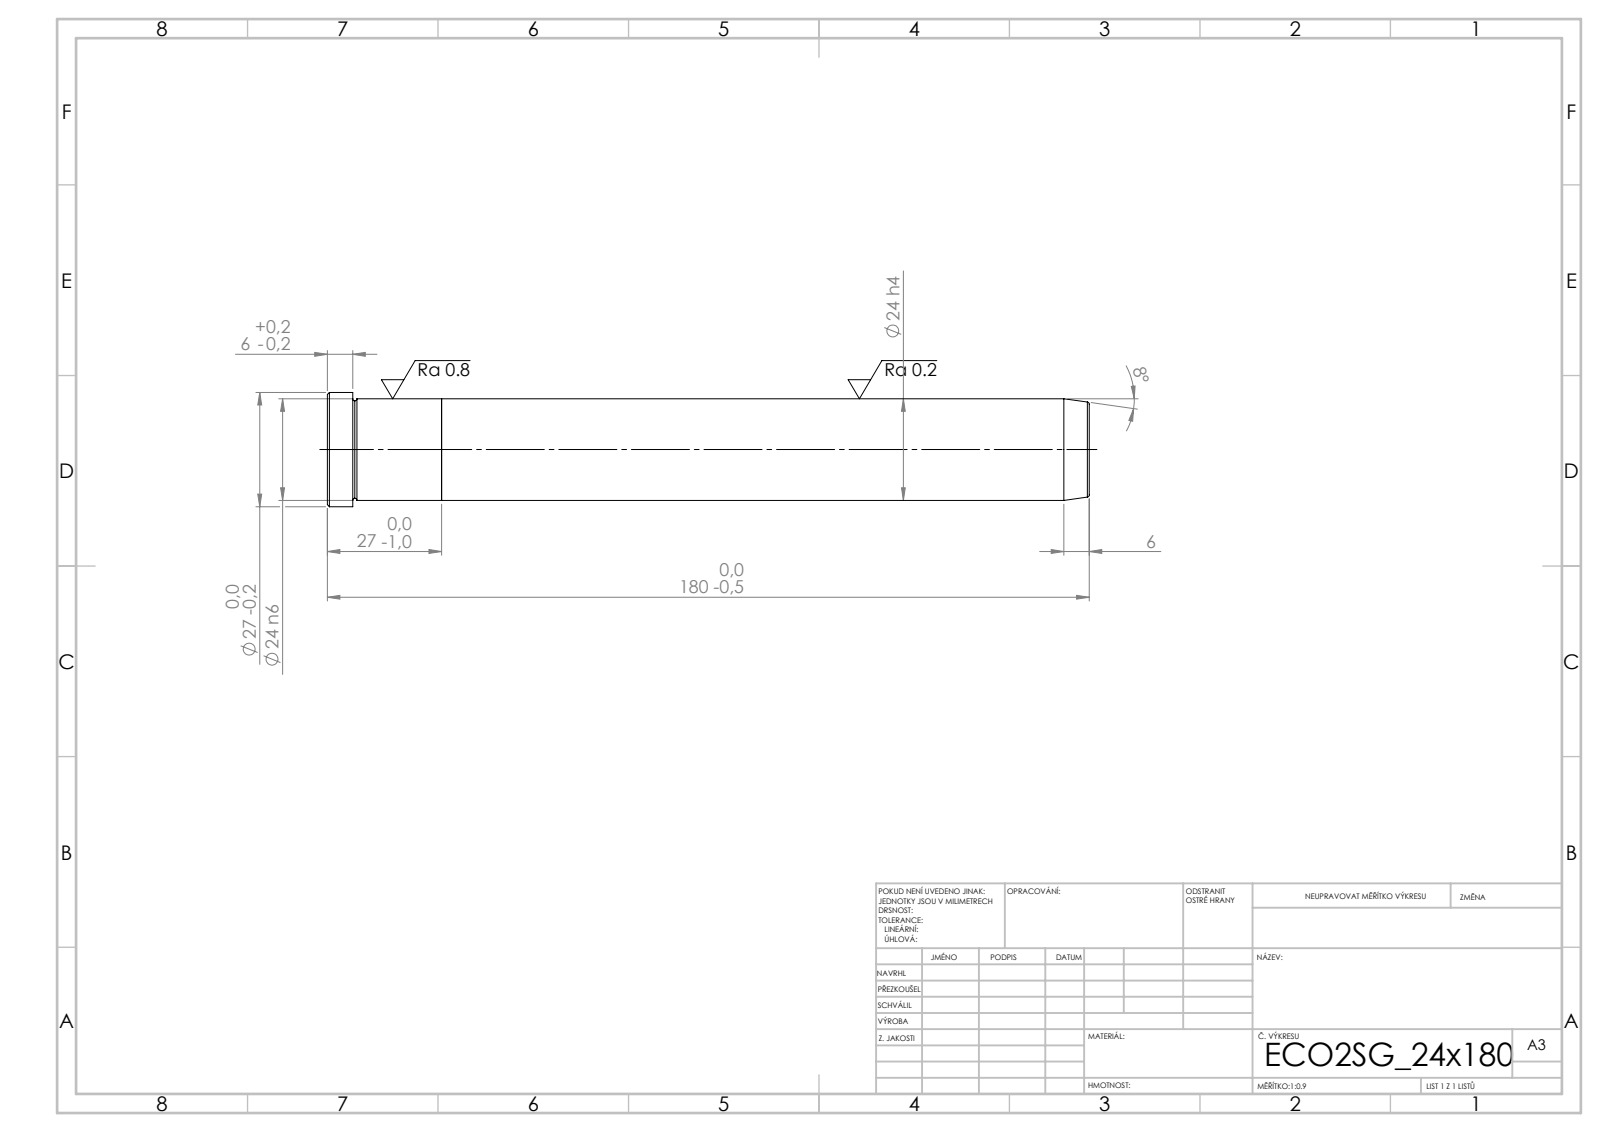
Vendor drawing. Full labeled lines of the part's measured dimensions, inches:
STEP written by: SolidWorks 2019 (CONFIG_CONTROL_DESIGN)
Units: inches
Bodies: 2 solids, 21 faces (5 planar, 6 cylindrical, 10 other)
Overall size (bounding box): 7.087 × 1.063 × 1.063
Volume: 4.999 in³ · Surface area: 24.19 in²
Round bosses / shafts (diameter × count): ⌀1.063 ×1, ⌀0.945 ×1
Main face-to-face distances: 1.063, 6.024, 7.087, 6.85, 0.827, 0.236
